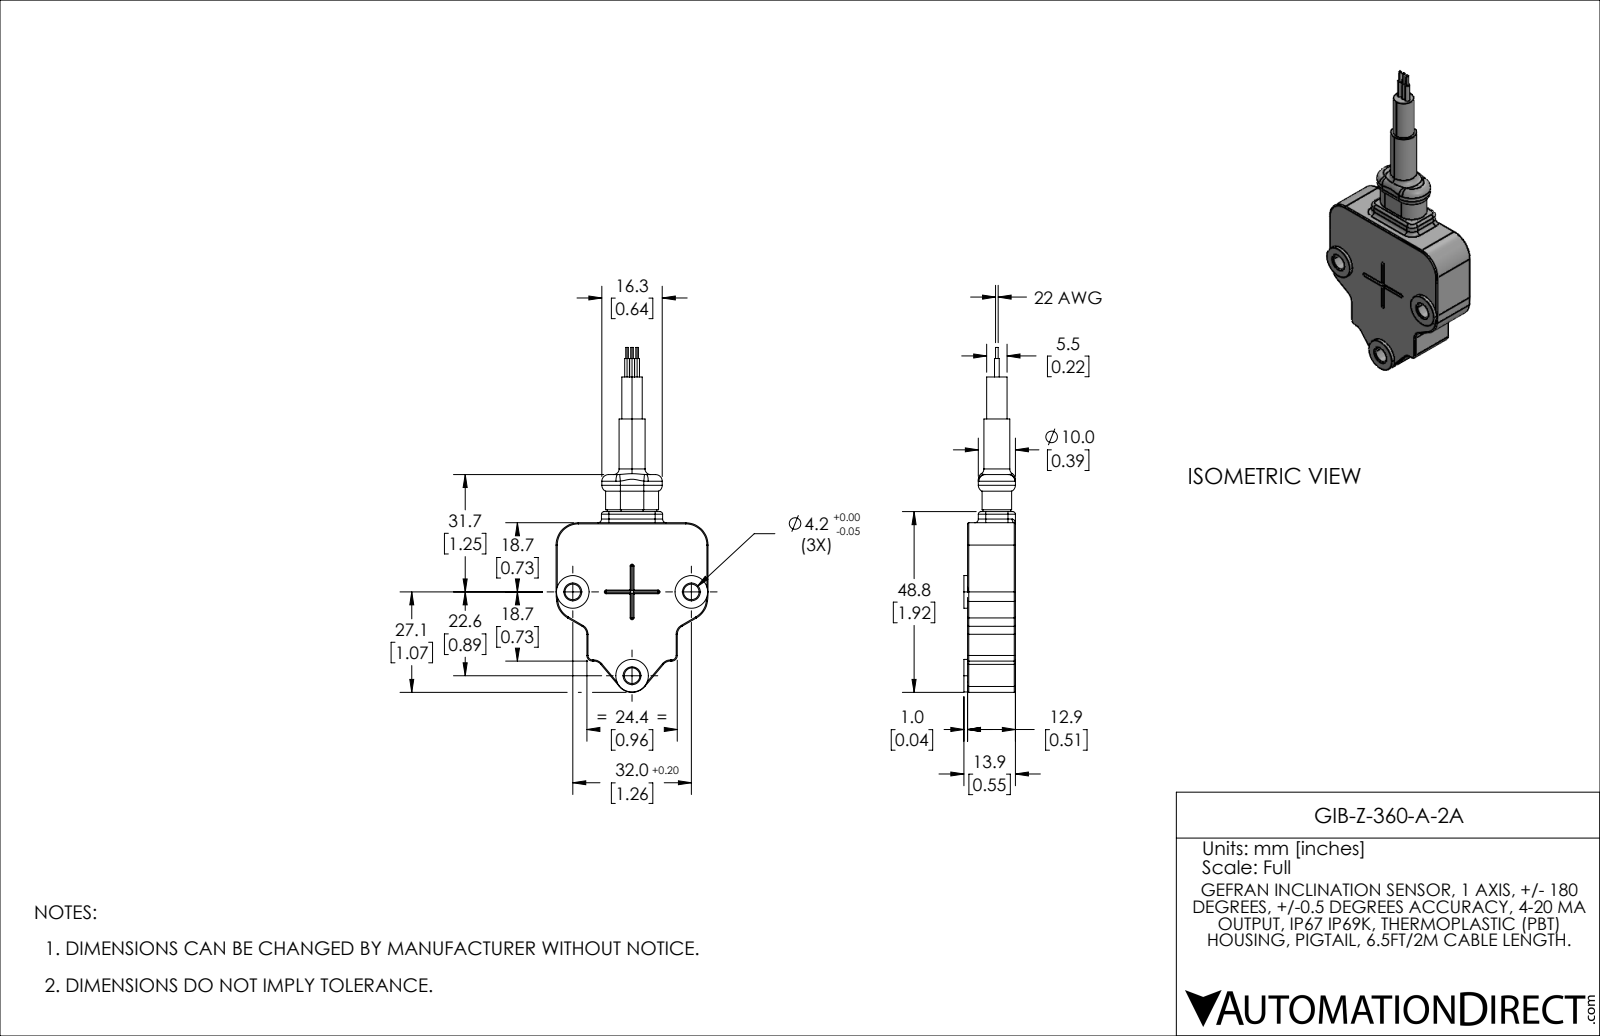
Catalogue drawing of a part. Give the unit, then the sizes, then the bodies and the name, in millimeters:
Units: millimetres
Overall size (bounding box): 93 × 41 × 13.9
Round holes (diameter × count): ⌀4.2 ×3
Round bosses / shafts (diameter × count): ⌀8.8 ×3, ⌀1.3 ×3, ⌀0.7 ×3, ⌀7 ×1, ⌀5.5 ×1
Partial cylindrical surfaces — rounded edges, fillets, slot ends (radius × count): R0.3 ×20, R0.2 ×4, R0.7 ×4, R2 ×4, R2.5 ×4, R6 ×4, R1 ×3, R1.5 ×2
Main face-to-face distances: 12.9, 1, 41, 8.3, 32.7, 13.9, 24.4, 9, 3.9, 3
Hole centre spacings: 27.7, 32
Volume: 20 420 mm³ · Surface area: 6 435 mm²
Bodies: 1 solid, 201 faces (47 planar, 87 cylindrical, 67 other)
Part name (STEP PRODUCT): GIB-Z-360-A-2A
STEP written by: SolidWorks 2021 (AUTOMOTIVE_DESIGN)
